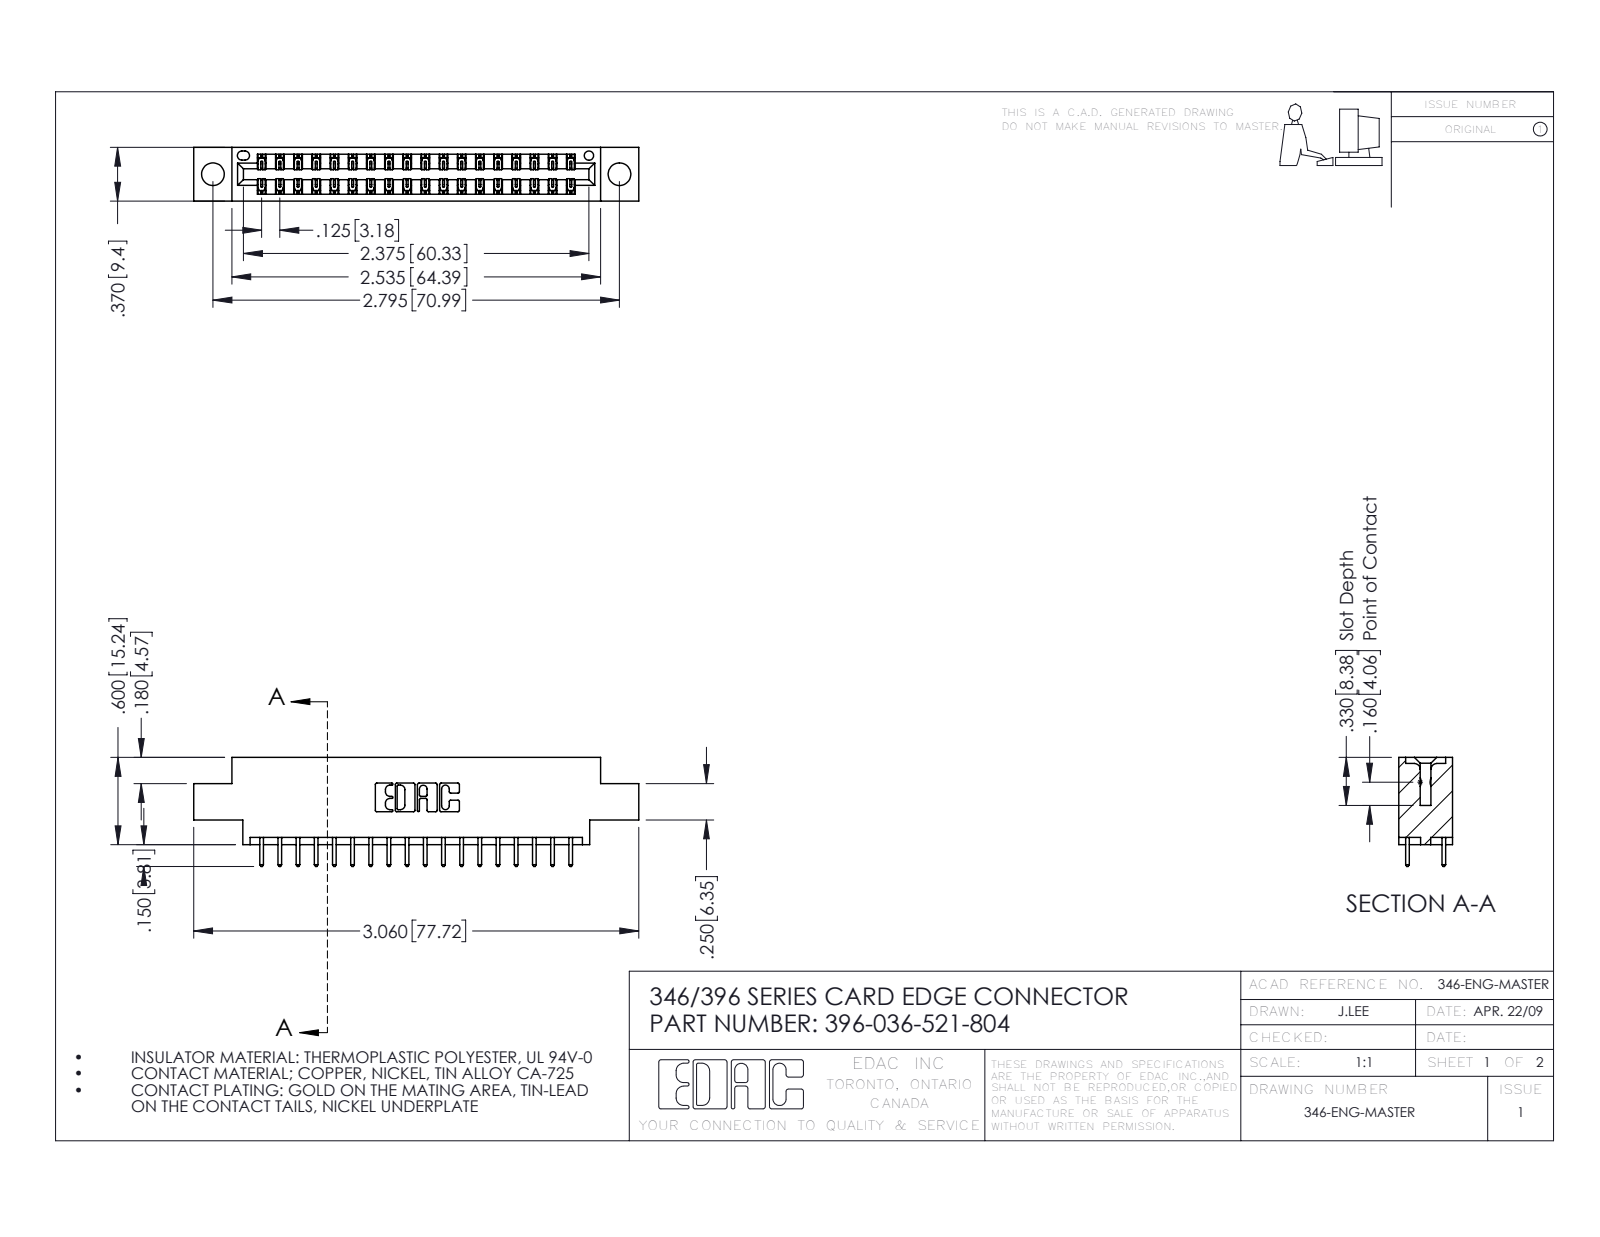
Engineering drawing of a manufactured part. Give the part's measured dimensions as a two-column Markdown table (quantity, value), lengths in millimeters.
| quantity | value |
| --- | --- |
| part name | 345-292-001_345-293-121; 346 Part_0.170 Offset - 0.156 Dia-TH; 396-036-521-804 |
| STEP written by | SolidWorks 2016 (CONFIG_CONTROL_DESIGN) |
| units | millimeters |
| bodies | 37 solids, 1998 faces (1340 planar, 658 cylindrical, 0 other) |
| overall size | 77.7 × 19.1 × 9.4 |
| volume | 7 130 mm³ |
| surface area | 9 323 mm² |
| round holes (diameter × count) | 4 × 2, 1.6 × 1 |
| partial cylindrical surfaces (radius × count) | 0.2 × 54, 0.3 × 36, 0.3 × 22, 0.2 × 6, 0.8 × 6, 0.7 × 3, 0.4 × 2, 0.6 × 2 |
| main face-to-face distances | 1.2, 8.2, 6.4, 9.4, 1.8, 7.6, 0.6, 7, 3.8, 5.6 |
| hole center spacings | 6.2, 65.7, 71 |
